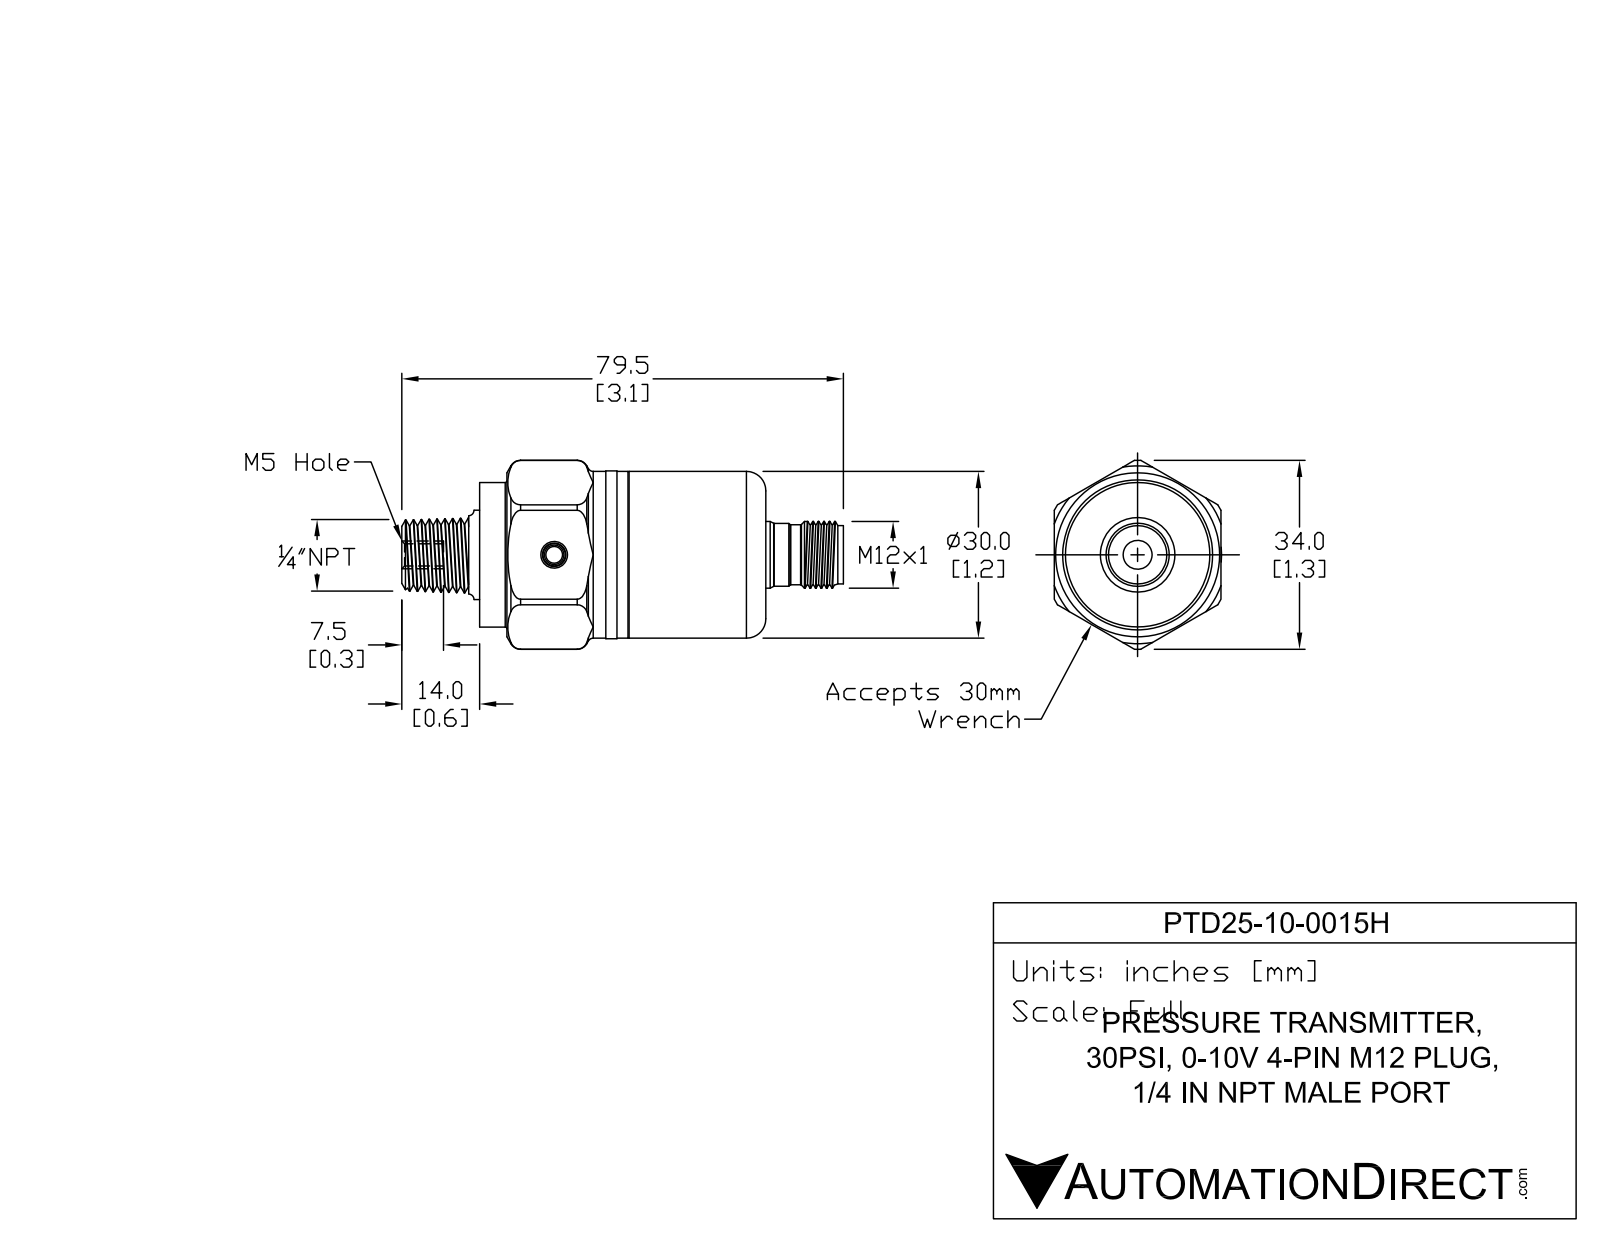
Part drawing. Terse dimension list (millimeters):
name: PTD25-10-0015H
written by: SolidWorks 2017 (AUTOMOTIVE_DESIGN)
unit: mm
bodies: 1 solid, 124 faces (36 planar, 59 cylindrical, 29 other)
size: 79.5 × 33.78 × 31.7
volume: 39 212 mm³; area: 8 088 mm²
holes: 1× ⌀4, 1× ⌀8.5
bosses: 1× ⌀30.05, 1× ⌀30, 1× ⌀25.96, 1× ⌀14, 1× ⌀13.5, 1× ⌀12
rounds: 1× R3.76, 1× R16.95
face distances: 51, 29.98, 30, 48, 3, 65, 17, 14, 30.01, 5.65
